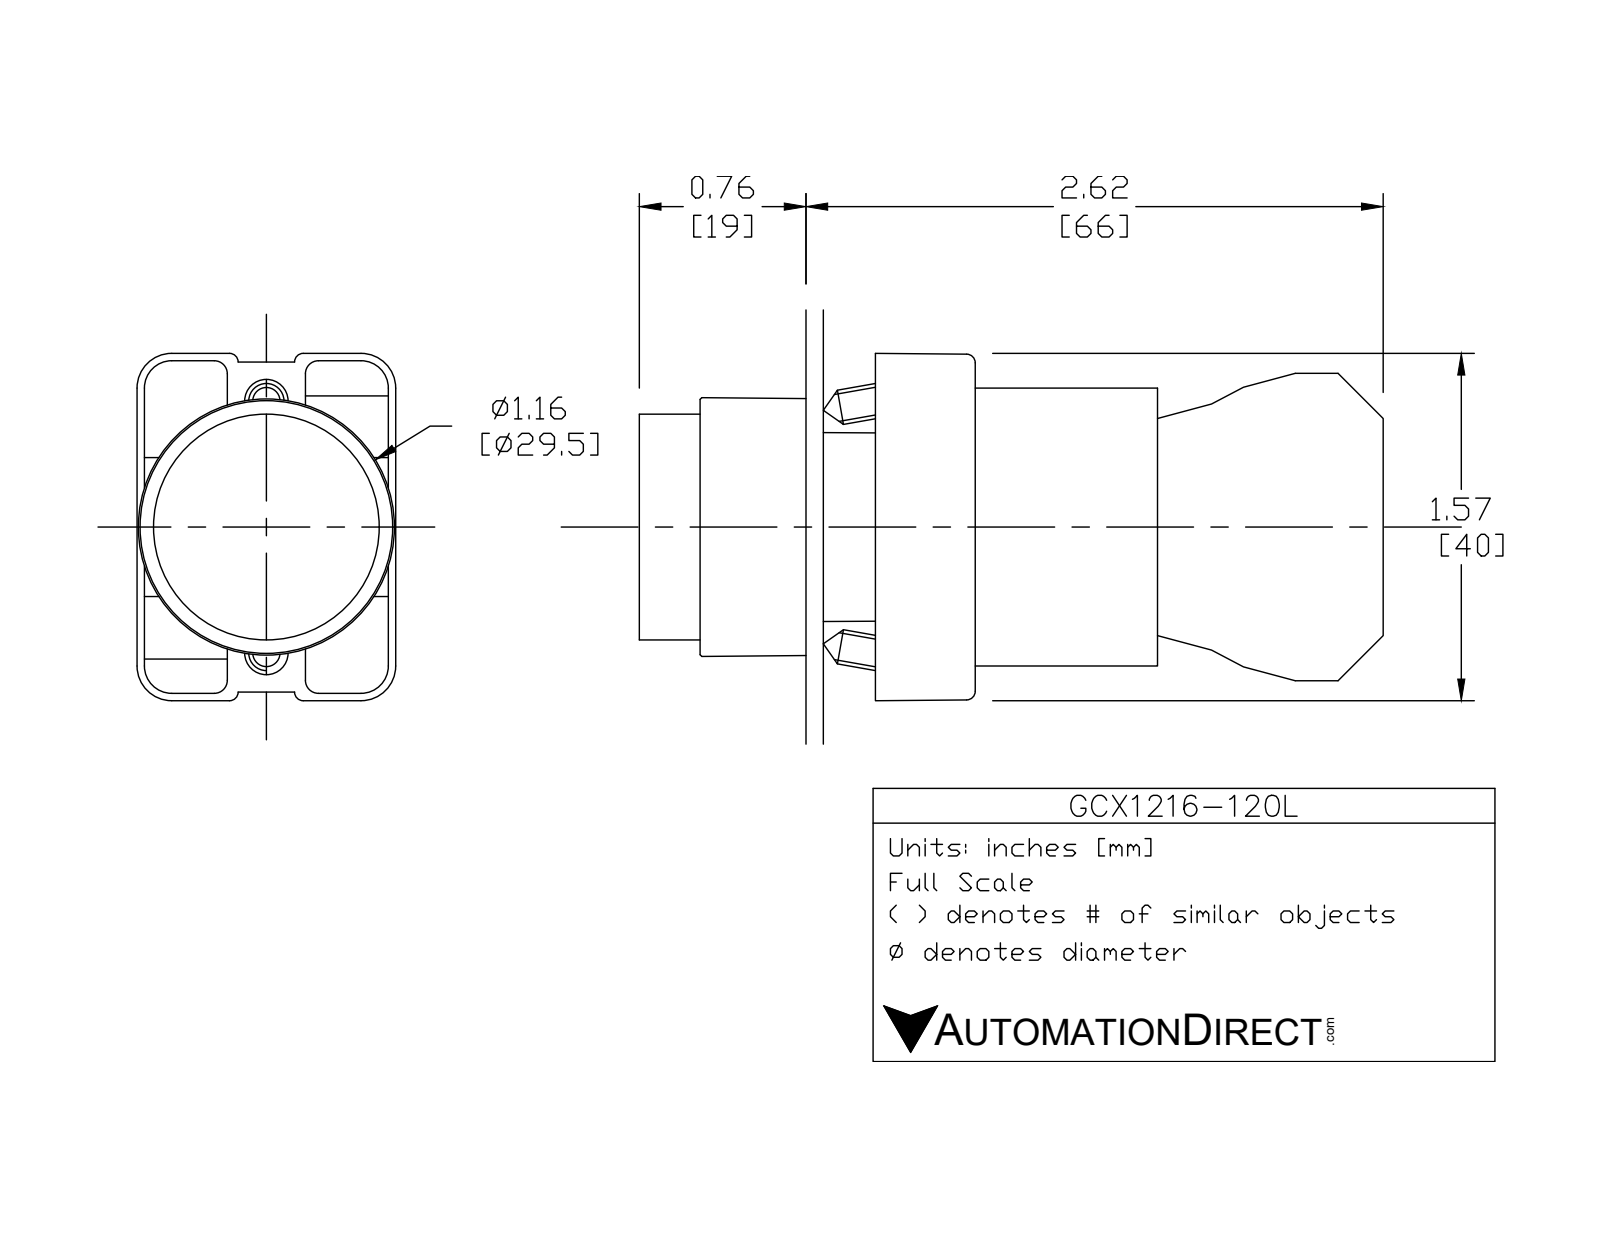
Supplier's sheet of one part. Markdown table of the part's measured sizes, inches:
| quantity | value |
| --- | --- |
| part name | ecx1040; ECX1050; GCX1216L OPERATOR; ecx1029 (+1 more) |
| STEP written by | SolidWorks 2016 (AUTOMOTIVE_DESIGN) |
| units | inches |
| bodies | 7 solids, 425 faces (250 planar, 144 cylindrical, 31 other) |
| overall size | 3.319 × 1.581 × 1.177 |
| volume | 2.721 in³ |
| surface area | 36.32 in² |
| round holes (diameter × count) | 0.079 × 2, 0.124 × 2, 0.13 × 2, 0.087 × 1, 0.197 × 1, 0.469 × 1, 0.878 × 1, 0.888 × 1, 1.024 × 1 |
| round bosses / shafts (diameter × count) | 0.157 × 4, 1.175 × 1, 1.004 × 1, 0.945 × 1, 0.856 × 1, 0.78 × 1, 0.504 × 1 |
| partial cylindrical surfaces (radius × count) | 0.059 × 24, 0.041 × 12, 0.124 × 12, 0.157 × 12, 0.039 × 8, 0.128 × 2, 0.02 × 1, 0.063 × 1 |
| main face-to-face distances | 0.827, 0.579, 1.171, 2.02, 1.193, 0.031, 0.033, 0.573, 1.165, 0.593 |
| hole center spacings | 0.236, 0.544, 0.472, 0.49 |
